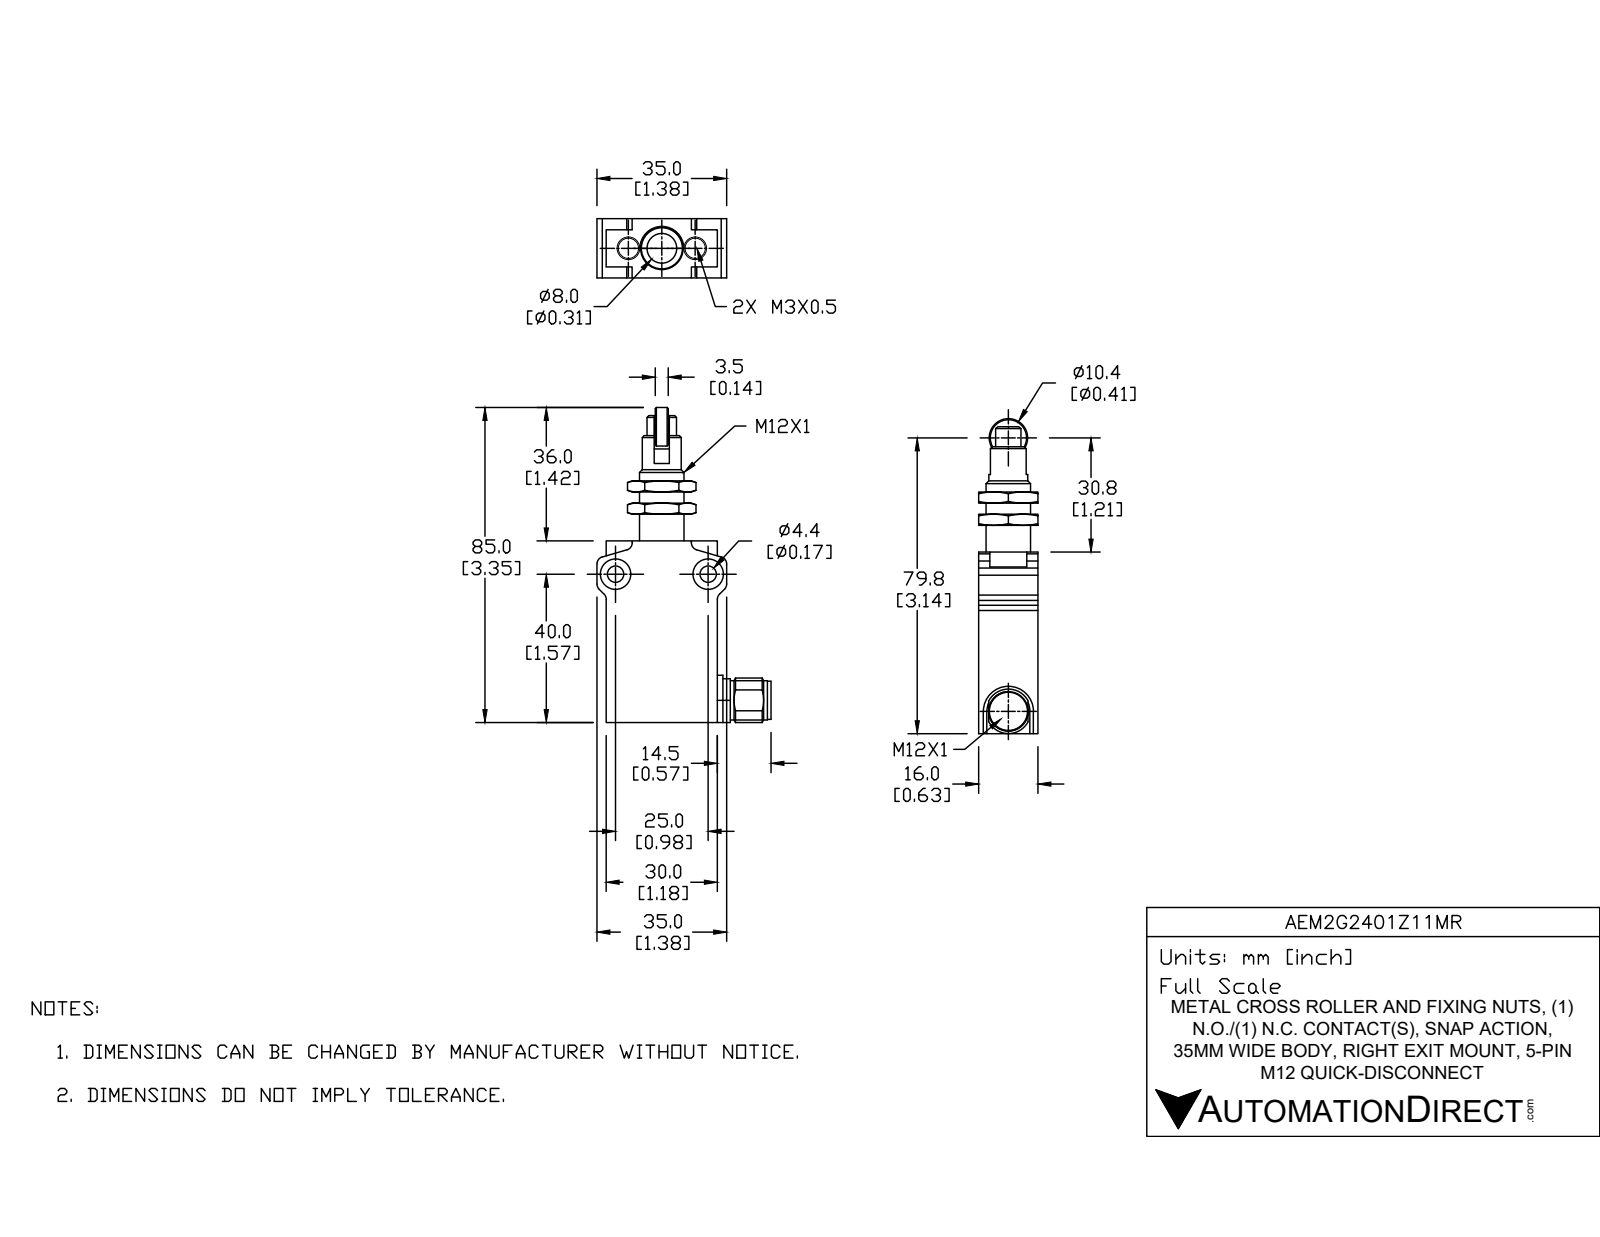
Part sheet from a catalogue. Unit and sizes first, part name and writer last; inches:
Units: inches
Overall size (bounding box): 3.465 × 1.831 × 0.727
Round holes (diameter × count): ⌀0.118 ×2, ⌀0.173 ×2, ⌀0.323 ×2, ⌀0.317 ×1, ⌀0.472 ×1
Round bosses / shafts (diameter × count): ⌀0.472 ×1, ⌀0.417 ×1, ⌀0.413 ×1, ⌀0.409 ×1, ⌀0.406 ×1, ⌀0.313 ×1, ⌀0.22 ×1
Partial cylindrical surfaces — rounded edges, fillets, slot ends (radius × count): R0.079 ×8, R0.256 ×1
Main face-to-face distances: 0.63, 1.181, 0.472, 0.118, 0.236, 2.047, 1.858, 0.189, 0.354, 0.157
Hole centre spacings: 0.374, 0.748, 0.984
Volume: 1.786 in³ · Surface area: 18.39 in²
Bodies: 7 solids, 199 faces (83 planar, 53 cylindrical, 63 other)
Part name (STEP PRODUCT): AEM2G2401Z11MR
STEP written by: SolidWorks 2019 (AUTOMOTIVE_DESIGN)
